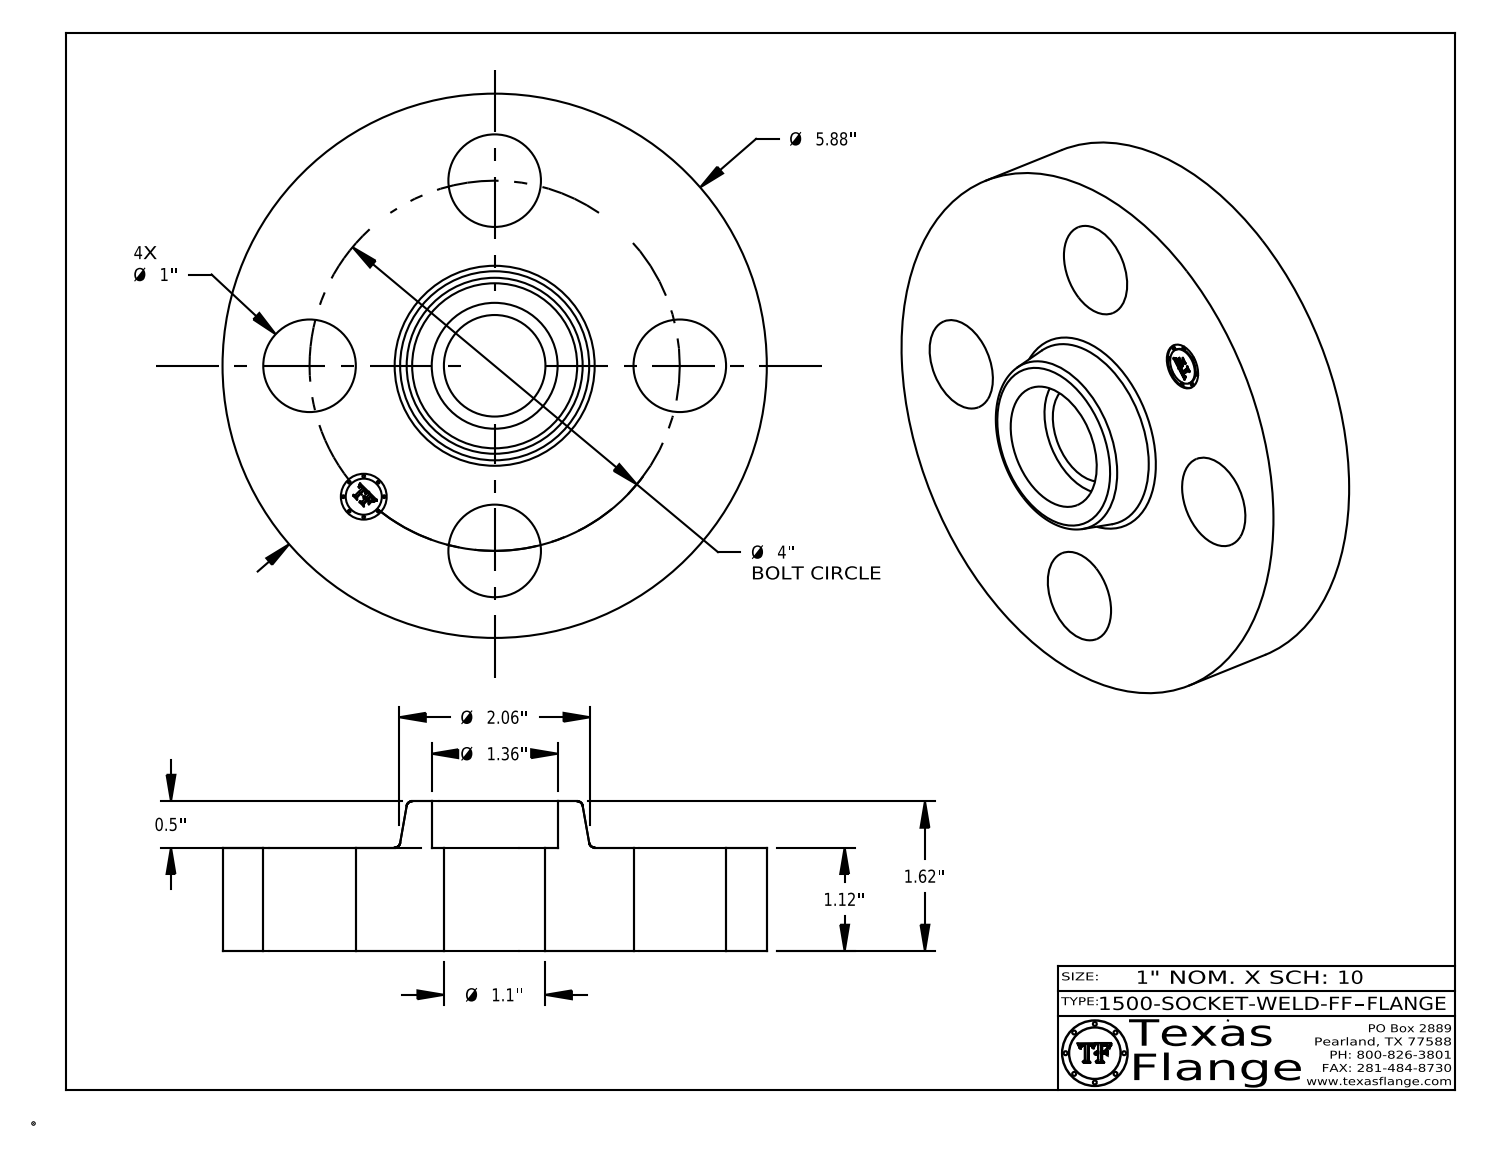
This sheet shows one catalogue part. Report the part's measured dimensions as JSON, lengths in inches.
{"part_name": "1500-SOCKET-WELD-FF", "step_written_by": "CATIA V5 STEP AP214 (AUTOMOTIVE_DESIGN)", "units": "inches", "bodies": {"solids": 1, "faces": 409, "planar": 369, "cylindrical": 34, "other": 6}, "overall_size": [5.88, 5.88, 1.62], "volume_in3": 26.64, "surface_area_in2": 89.38, "round_holes": [[1, 4], [0.495, 1], [1.097, 1], [1.36, 1]], "round_bosses_or_shafts": [[0.03, 8], [5.88, 1], [0.39, 1]], "face_to_face_distances": [1.12, 1.62, 0.5, 0.015, 1.105, 0.515, 0.148, 0.145, 0.027, 0.096], "hole_center_spacings": [2, 2.828, 1.531, 3.695, 4]}
